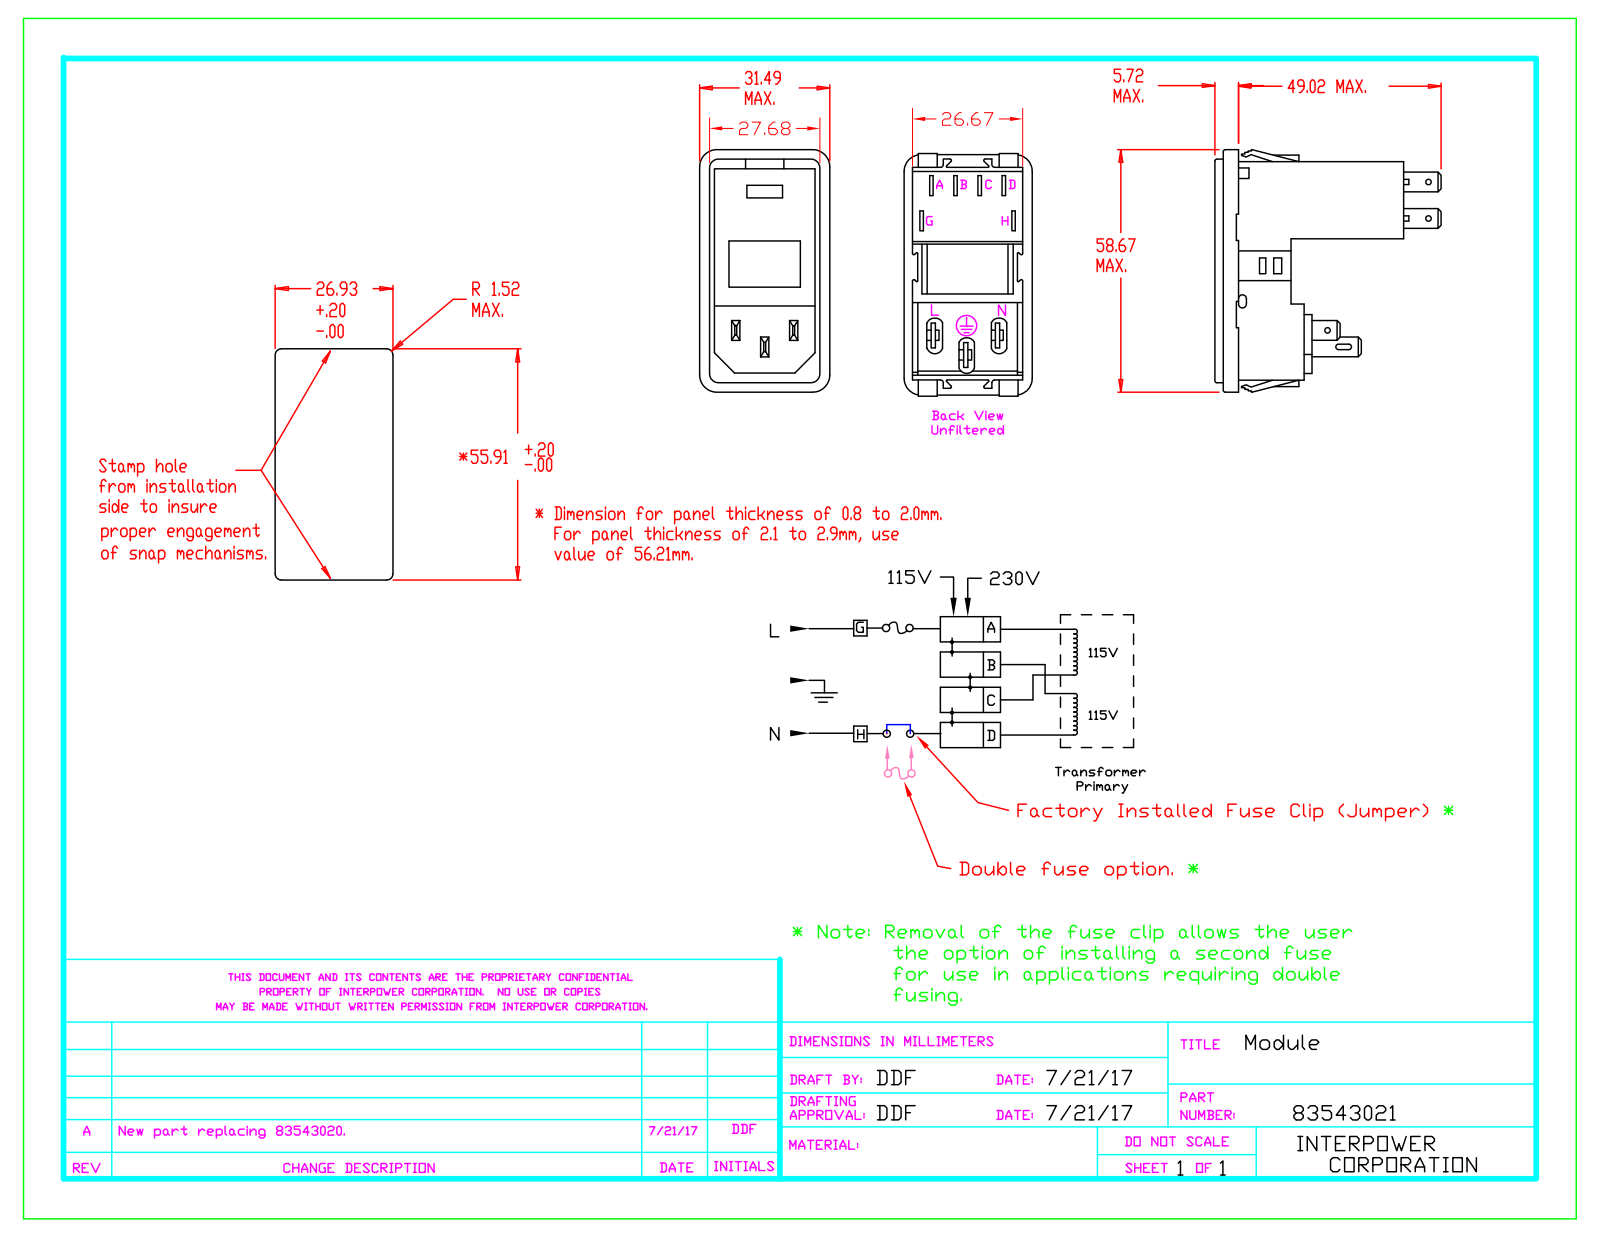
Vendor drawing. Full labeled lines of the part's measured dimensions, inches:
Part name (STEP PRODUCT): 83543020-R1
STEP written by: SolidWorks 2007 (CONFIG_CONTROL_DESIGN)
Units: inches
Bodies: 1 solid, 571 faces (451 planar, 60 cylindrical, 60 other)
Overall size (bounding box): 2.343 × 2.155 × 1.24
Volume: 2.01 in³ · Surface area: 24.75 in²
Round holes (diameter × count): ⌀0.052 ×3, ⌀0.089 ×1
Round bosses / shafts (diameter × count): ⌀0.108 ×1
Partial cylindrical surfaces — rounded edges, fillets, slot ends (radius × count): R0.039 ×19, R0.02 ×8, R0.085 ×4, R0.165 ×4, R0.026 ×2, R0.03 ×2
Main face-to-face distances: 1.024, 0.734, 0.05, 0.225, 0.64, 0.019, 1.573, 1.798, 1.374, 0.425
Hole centre spacings: 0.347, 1.436, 1.71
